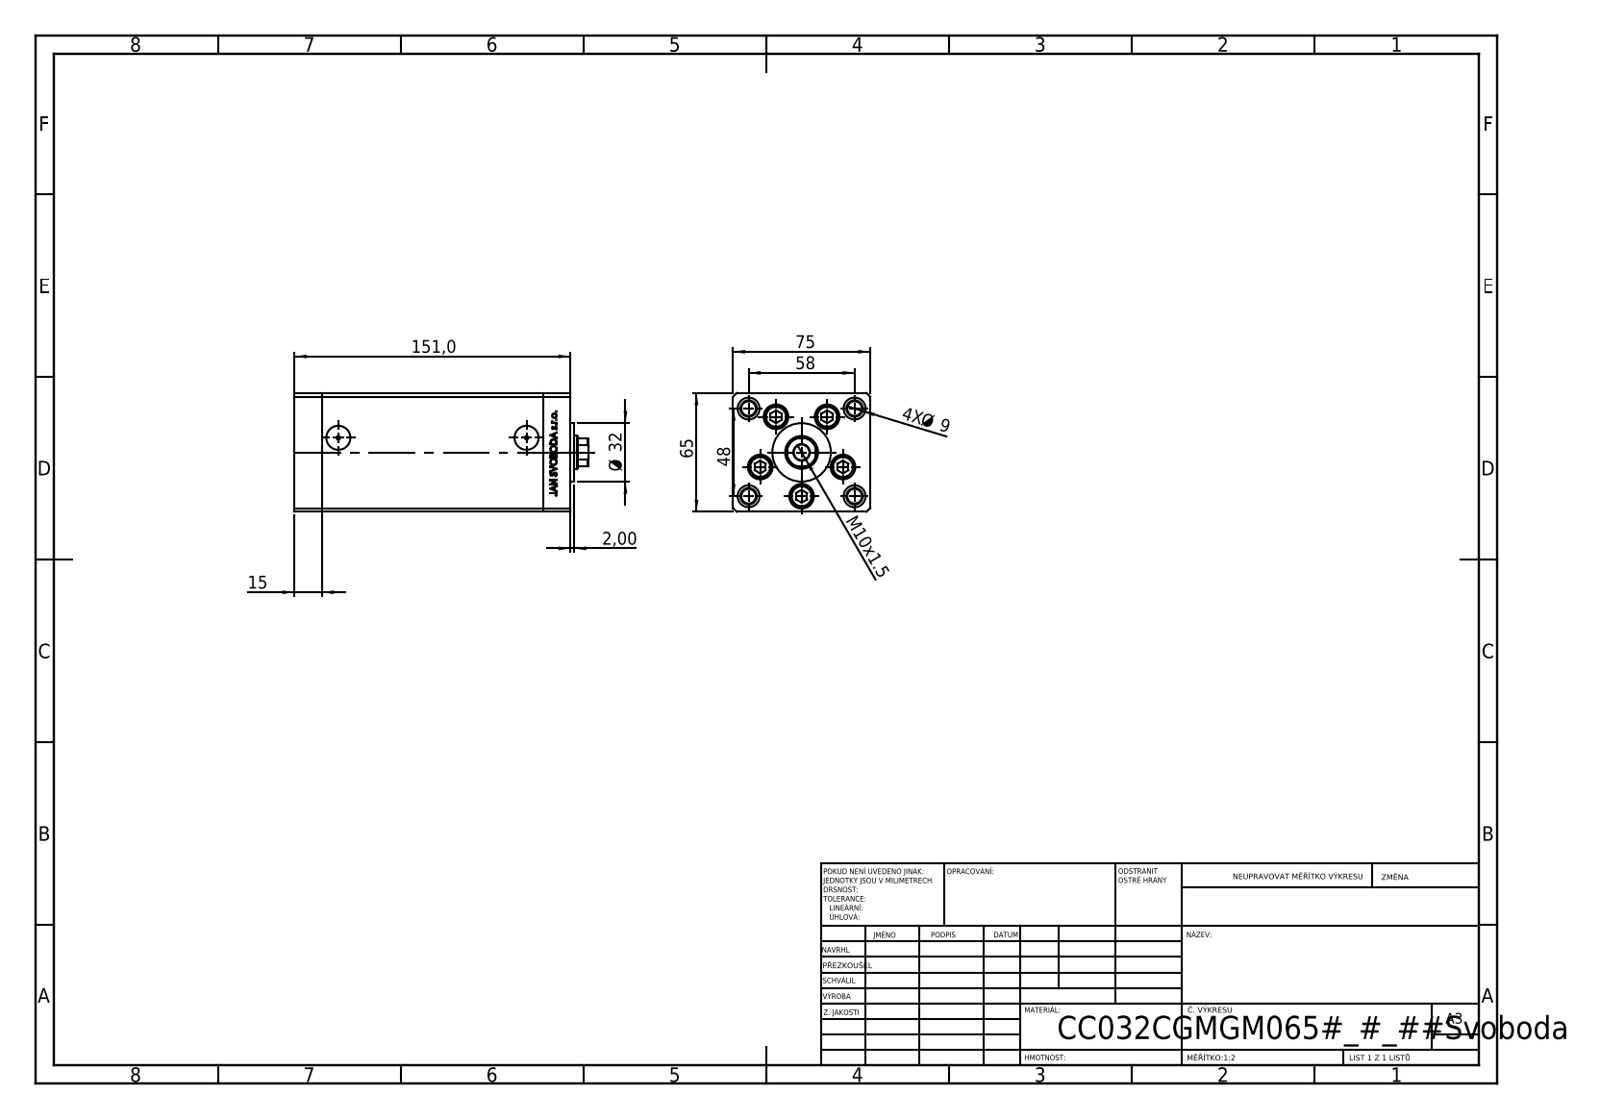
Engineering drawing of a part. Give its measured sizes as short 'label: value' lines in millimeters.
name: V220C_C MIDDLE; ALLEN BOLT; V220C_VC_C; V220C FRONT (+1 more)
written by: SolidWorks 2019 (CONFIG_CONTROL_DESIGN)
unit: mm
bodies: 12 solids, 1169 faces (540 planar, 167 cylindrical, 462 other)
size: 161 × 75 × 65
volume: 557 972 mm³; area: 133 975 mm²
holes: 9× ⌀9, 5× ⌀13.5, 4× ⌀8, 4× ⌀12, 2× ⌀2, 2× ⌀13.16, 1× ⌀8.5, 1× ⌀12.5, 1× ⌀18
bosses: 5× ⌀8, 4× ⌀12.5, 1× ⌀32
rounds: 2× R0.93, 1× R8.5
face distances: 75, 65, 15, 121, 136, 151, 28, 127, 13, 9
hole spacings: 24, 37.64, 15.67, 17.22, 27.71, 28.83, 29, 32.63
